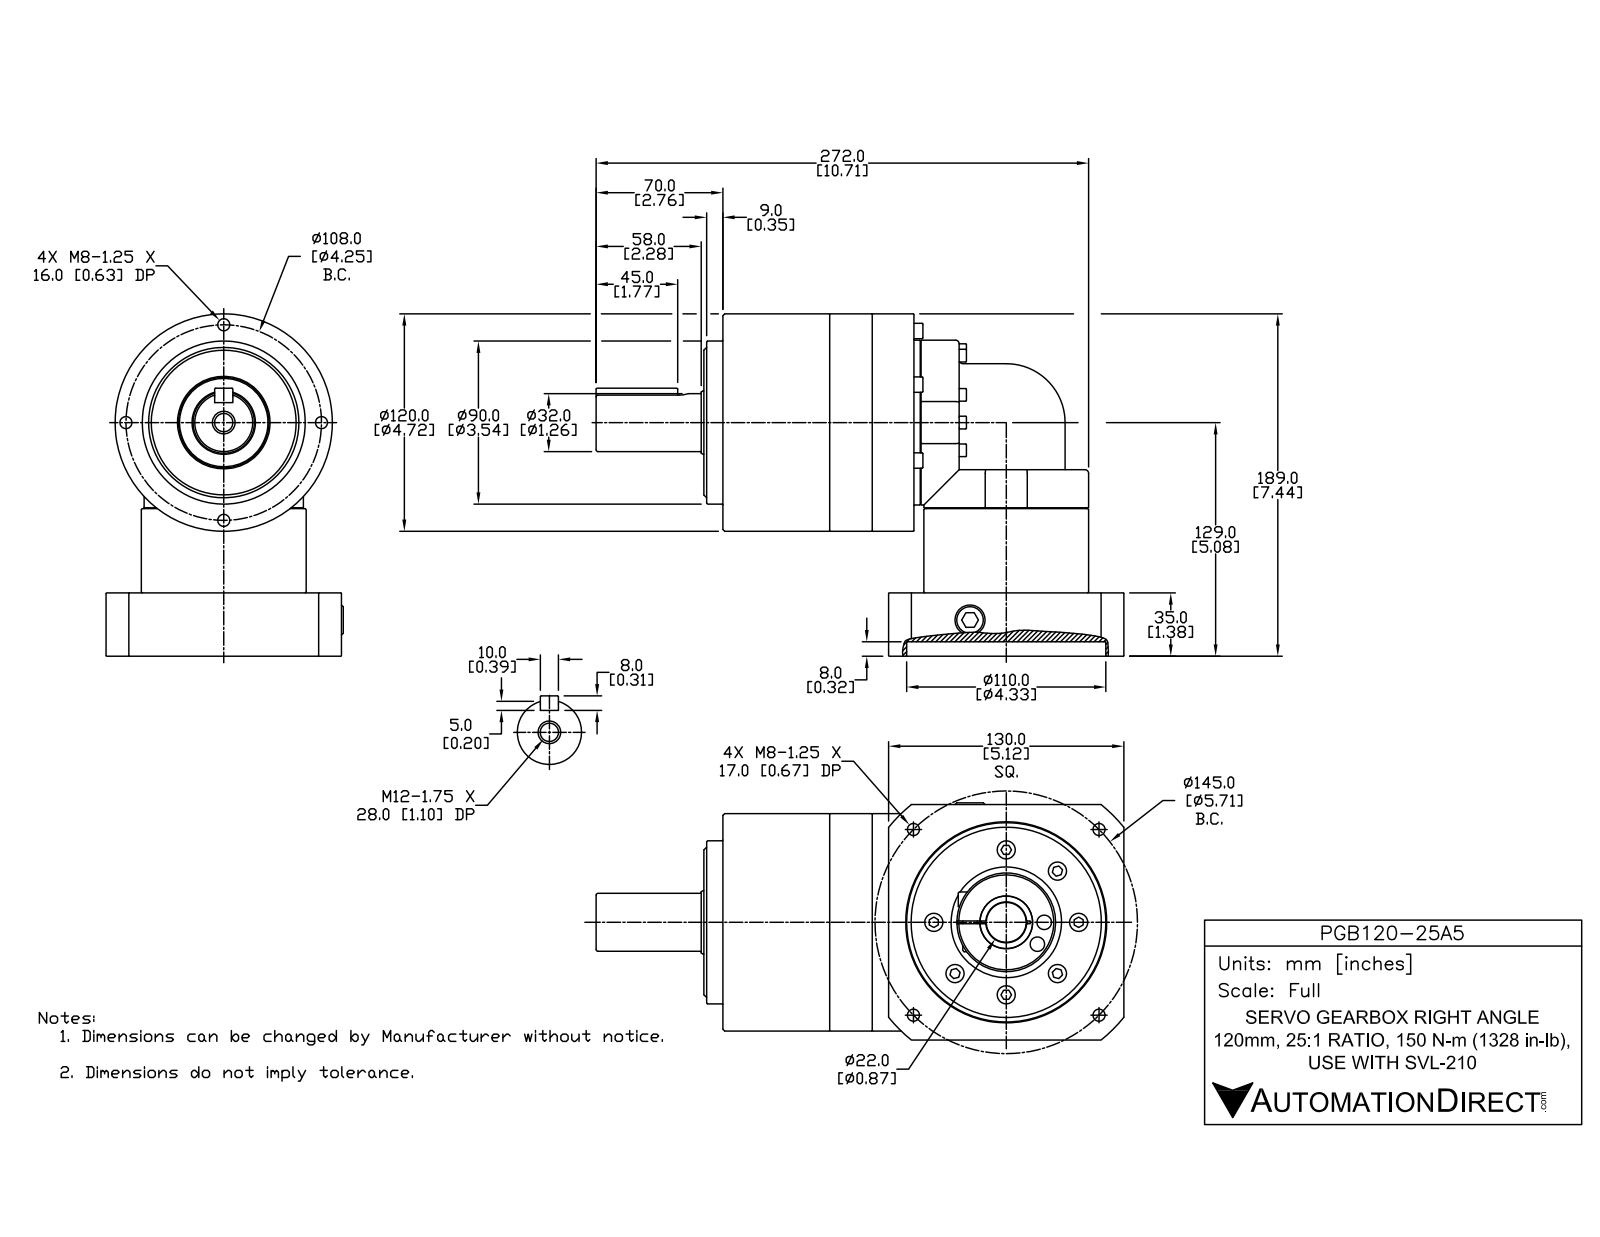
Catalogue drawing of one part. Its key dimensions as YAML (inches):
part_name: "PGB120-25A5"
step_written_by: "SolidWorks 2014 (AUTOMOTIVE_DESIGN)"
units: inches
bodies: {solids: 2, faces: 652, planar: 277, cylindrical: 160, other: 215}
overall_size: [11.476, 7.441, 5.157]
volume: 145.3
surface_area: 298.2
round_holes:
  - {diameter: 0.262, count: 7}
  - {diameter: 0.217, count: 6}
  - {diameter: 0.315, count: 2}
  - {diameter: 0.262, count: 1}
  - {diameter: 0.346, count: 1}
  - {diameter: 0.398, count: 1}
  - {diameter: 0.561, count: 1}
  - {diameter: 0.866, count: 1}
  - {diameter: 2.402, count: 1}
  - {diameter: 4.134, count: 1}
  - {diameter: 4.331, count: 1}
round_bosses_or_shafts:
  - {diameter: 0.276, count: 9}
  - {diameter: 0.394, count: 7}
  - {diameter: 0.335, count: 6}
  - {diameter: 0.197, count: 6}
  - {diameter: 3.583, count: 2}
  - {diameter: 4.724, count: 1}
  - {diameter: 3.543, count: 1}
  - {diameter: 3.465, count: 1}
partial_cylinders:
  - {radius: 0.079, count: 6}
  - {radius: 1.28, count: 2}
  - {radius: 0.131, count: 1}
  - {radius: 0.197, count: 1}
  - {radius: 0.276, count: 1}
  - {radius: 3.287, count: 1}
face_to_face_distances: [0.02, 4.567, 5.118, 1.378, 4.291, 0.236, 1.142, 0.157, 0.689, 4.154]
hole_center_spacings: [0.836, 2.156, 2.379, 3.56, 4.199, 1.65, 2.126, 2.855]
